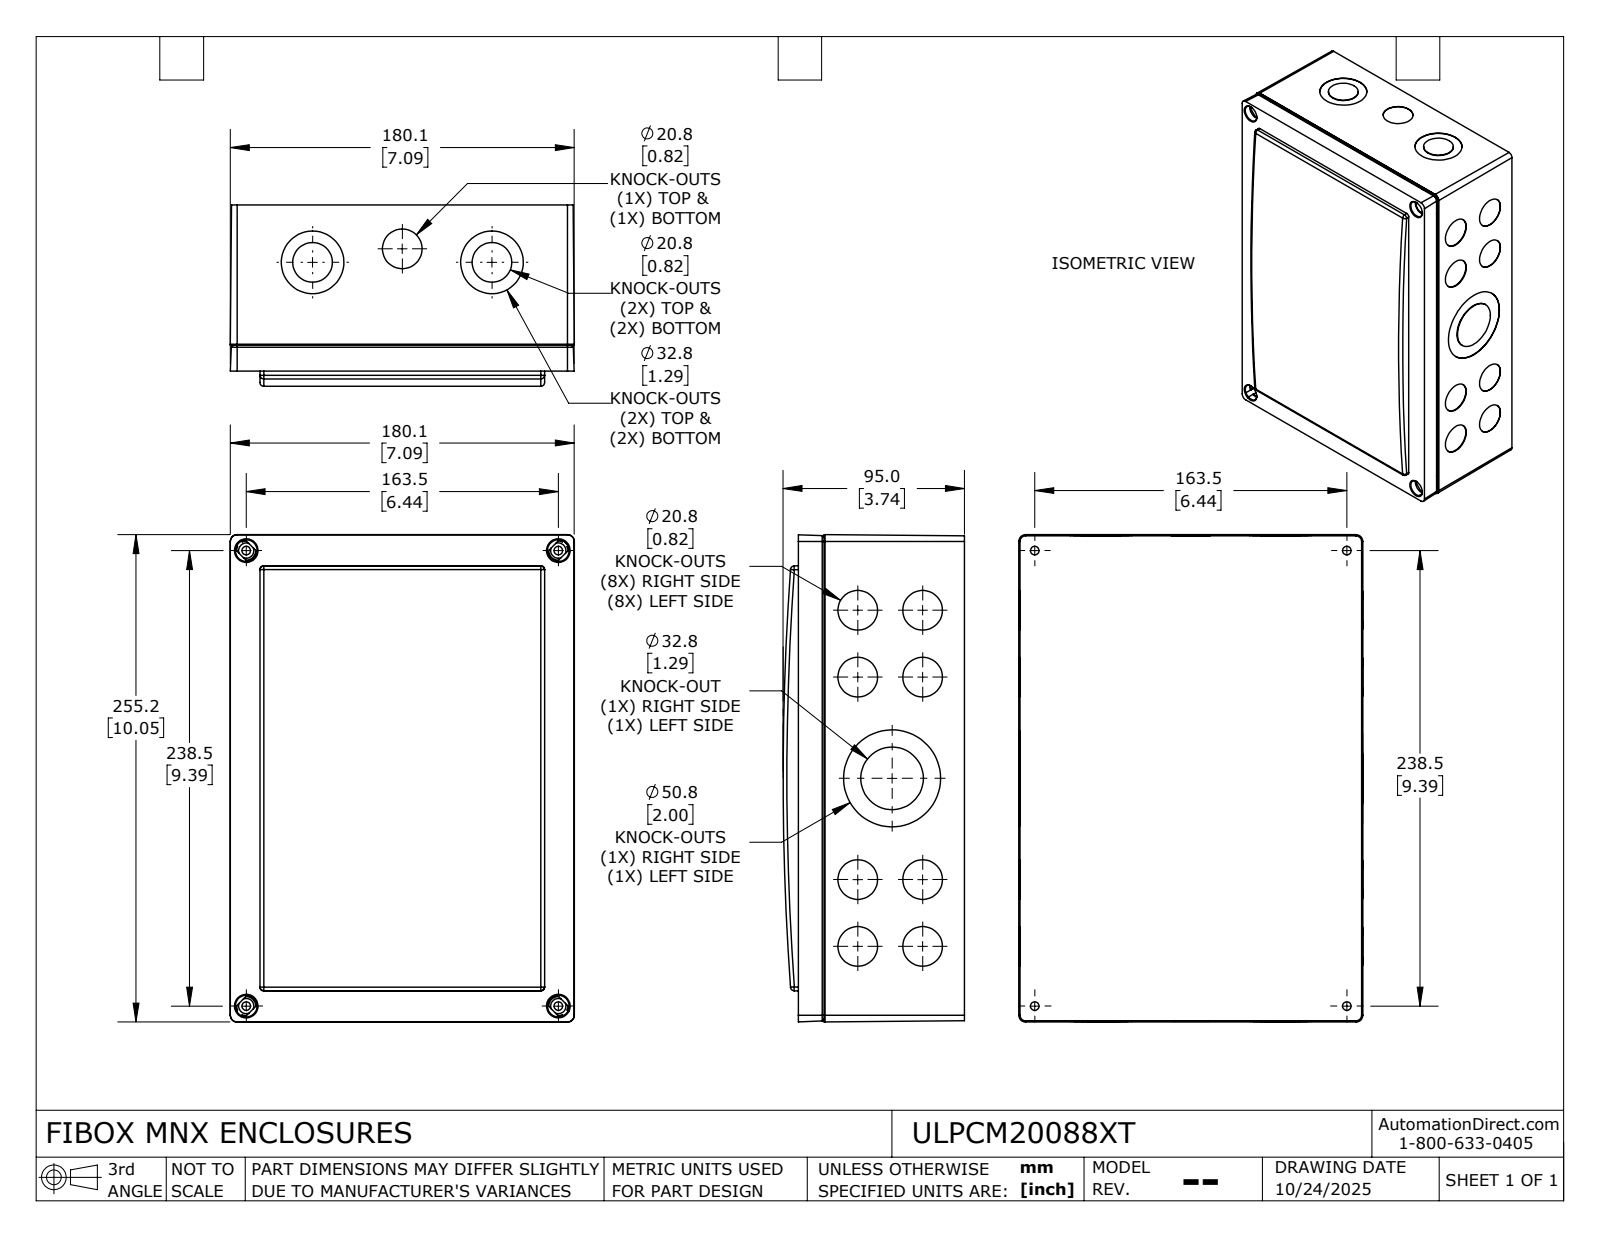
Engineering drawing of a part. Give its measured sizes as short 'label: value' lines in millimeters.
name: ULPCM20088XT
written by: SolidWorks 2024 (AUTOMOTIVE_DESIGN)
unit: mm
bodies: 2 solids, 339 faces (177 planar, 122 cylindrical, 40 other)
size: 255.17 × 180.17 × 95
volume: 709 907 mm³; area: 340 472 mm²
holes: 20× ⌀3.2, 4× ⌀4.5, 4× ⌀8, 2× ⌀11.34, 1× ⌀11.38, 1× ⌀11.39
bosses: 12× ⌀7.19, 8× ⌀9.18, 8× ⌀2.52
rounds: 12× R2, 8× R1.38, 8× R4.02, 4× R2.9, 4× R3.5, 4× R5, 4× R5.58, 4× R8.22
face distances: 3, 14, 70, 73, 87, 84, 147.91, 0.5, 73.5, 70.5
hole spacings: 49.24, 128.16, 125, 20.62, 22.15, 26.58, 33.85, 38.3
